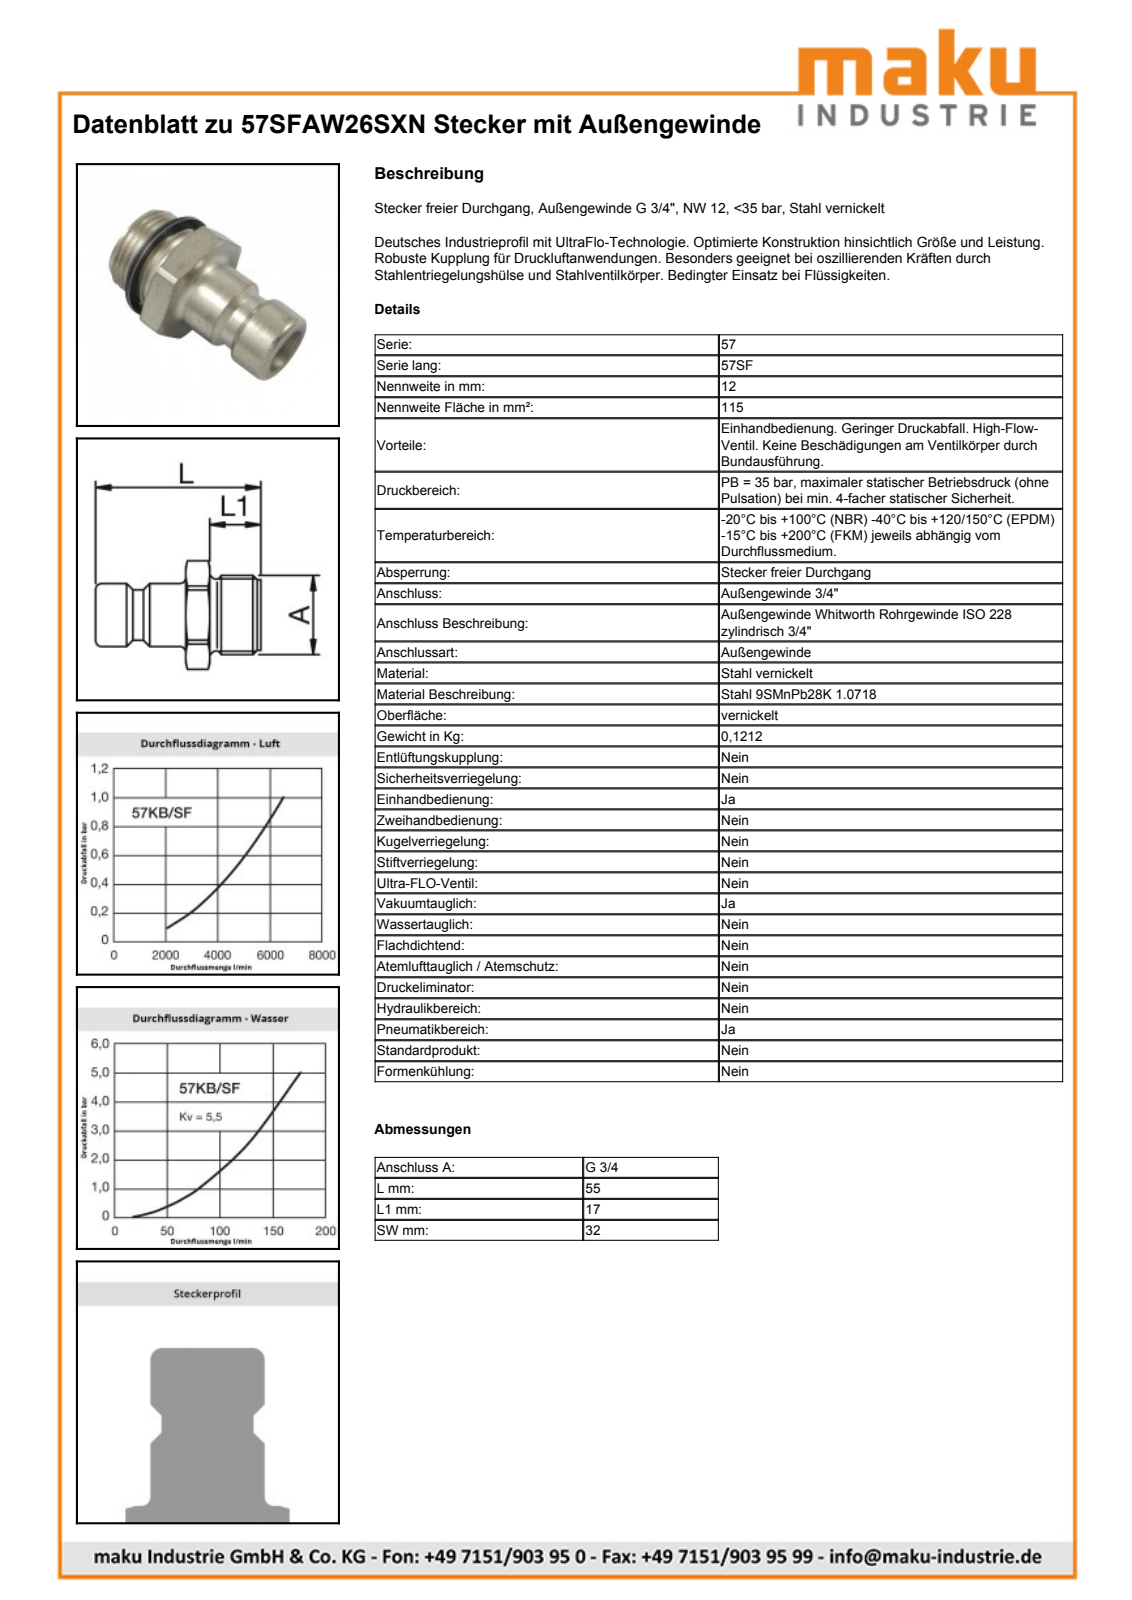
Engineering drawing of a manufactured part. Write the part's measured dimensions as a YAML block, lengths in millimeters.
part_name: "D107018; D106970; D103699"
step_written_by: "Autodesk Inventor 2013 (AUTOMOTIVE_DESIGN)"
units: millimeters
bodies: {solids: 2, faces: 55, planar: 15, cylindrical: 17, other: 23}
overall_size: [55, 36.1, 32]
volume: 16621
surface_area: 8855
round_holes:
  - {diameter: 13.5, count: 1}
  - {diameter: 16, count: 1}
round_bosses_or_shafts:
  - {diameter: 32, count: 1}
  - {diameter: 26.44, count: 1}
  - {diameter: 23.5, count: 1}
  - {diameter: 20.9, count: 1}
  - {diameter: 16.8, count: 1}
partial_cylinders:
  - {radius: 13.3, count: 1}
  - {radius: 18.05, count: 1}
face_to_face_distances: [32, 8, 10, 2, 25, 17, 15, 30, 38, 40]
